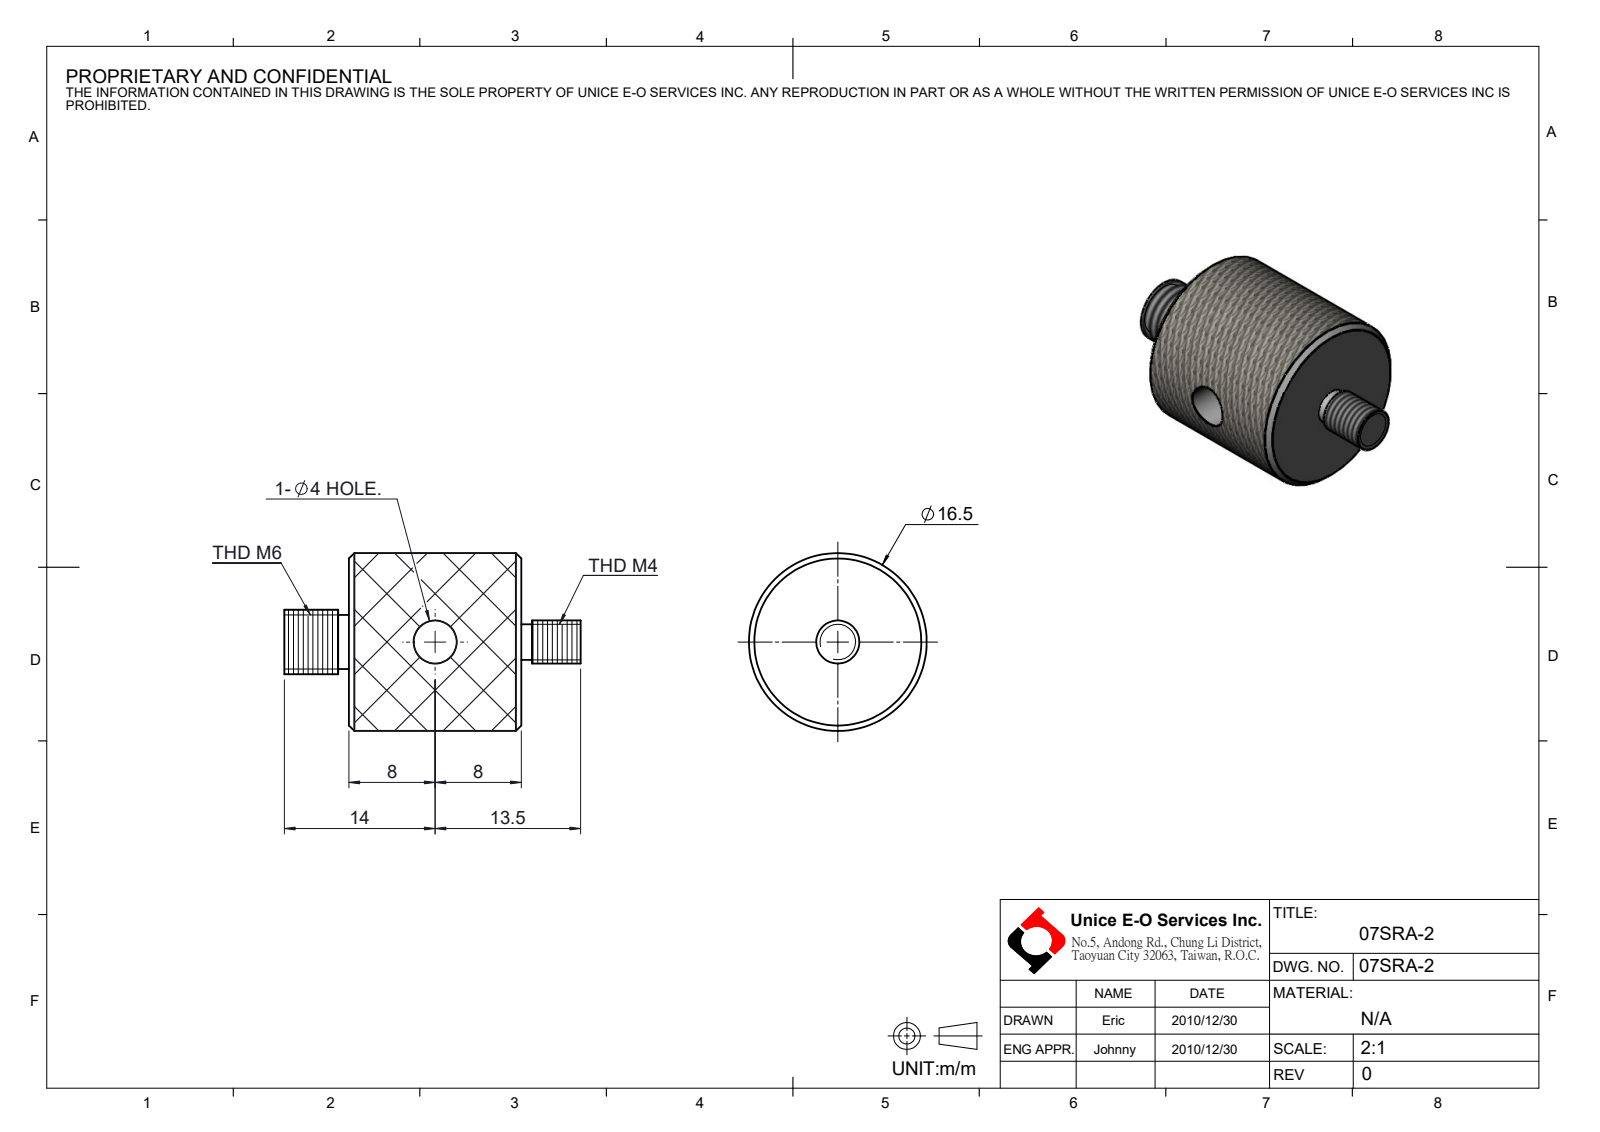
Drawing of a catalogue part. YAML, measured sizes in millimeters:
part_name: "07SRA-2"
step_written_by: "SolidWorks 2016 (CONFIG_CONTROL_DESIGN)"
units: millimeters
bodies: {solids: 1, faces: 22, planar: 6, cylindrical: 12, other: 4}
overall_size: [27.5, 16.5, 16.5]
volume: 3429
surface_area: 1607
round_holes:
  - {diameter: 4, count: 1}
round_bosses_or_shafts:
  - {diameter: 16.5, count: 1}
  - {diameter: 6, count: 1}
  - {diameter: 5, count: 1}
  - {diameter: 4, count: 1}
  - {diameter: 3.3, count: 1}
face_to_face_distances: [16, 22, 6, 1, 17, 5.5, 21.5, 27.5, 22.5, 5]
